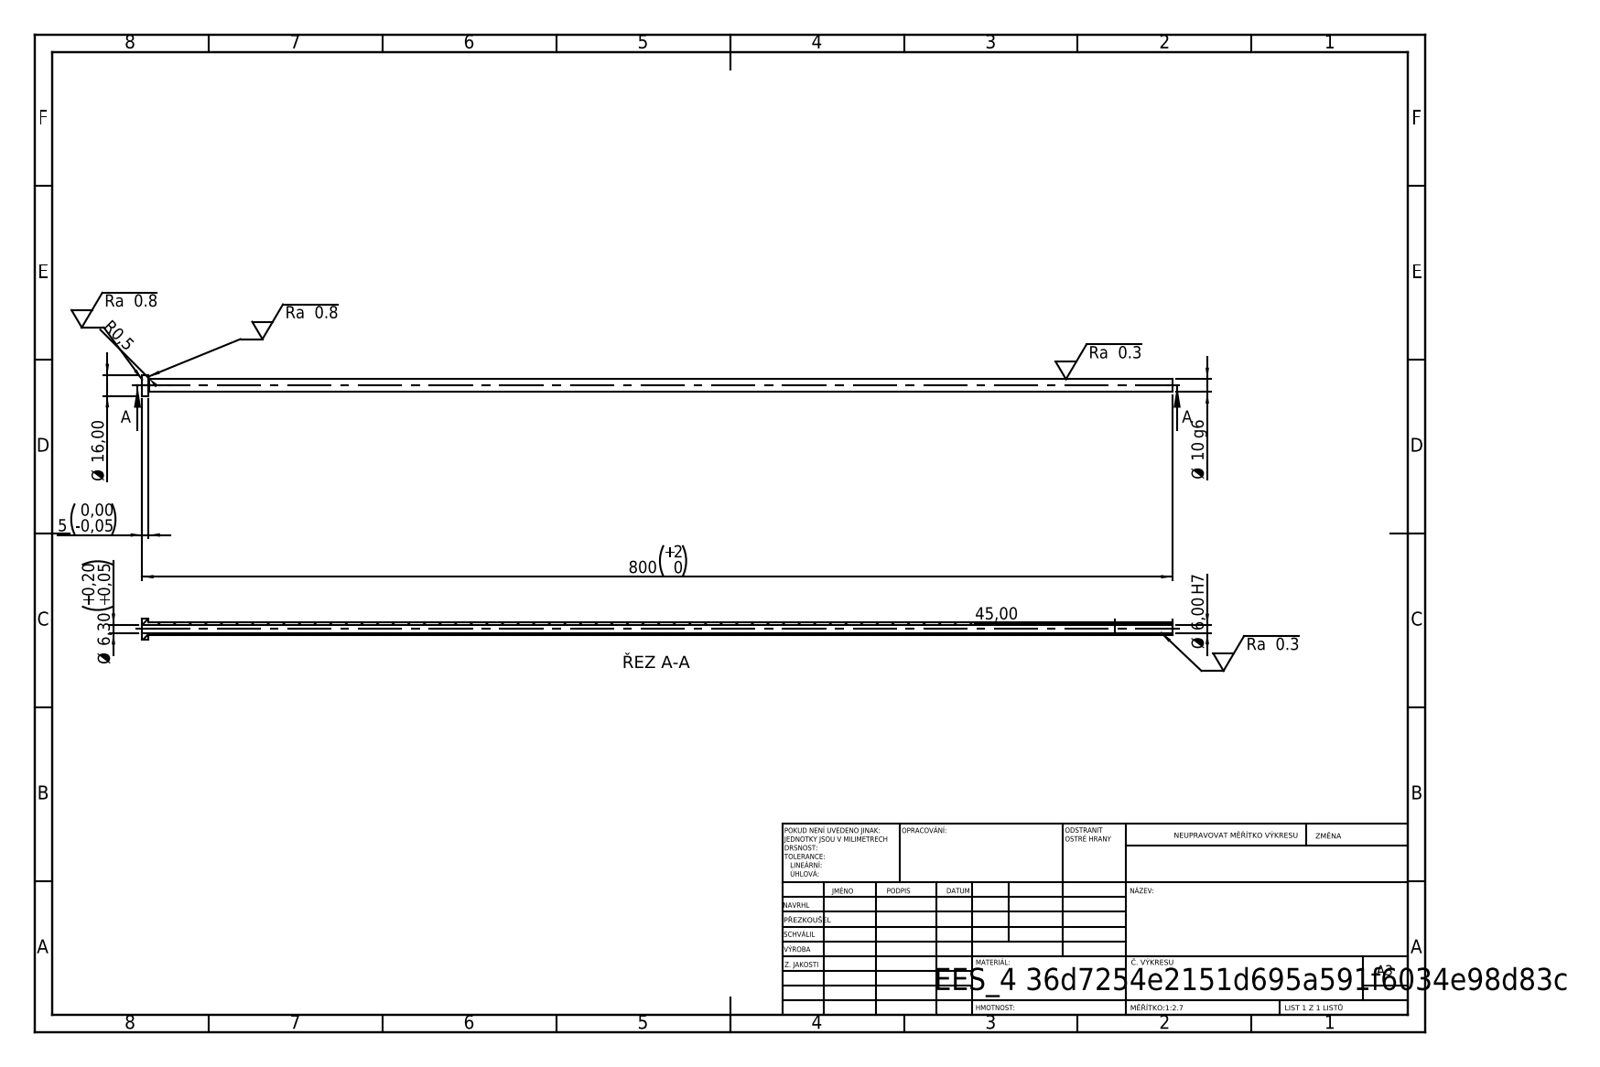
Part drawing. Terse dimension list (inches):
written by: SolidWorks 2019 (CONFIG_CONTROL_DESIGN)
unit: in
bodies: 1 solid, 14 faces (4 planar, 8 cylindrical, 2 other)
size: 31.496 × 0.63 × 0.63
volume: 2.358 in³; area: 64.1 in²
holes: 1× ⌀0.236, 1× ⌀0.248
bosses: 1× ⌀0.63, 1× ⌀0.394
face distances: 0.197, 31.496, 31.299, 29.724, 29.528, 1.772
